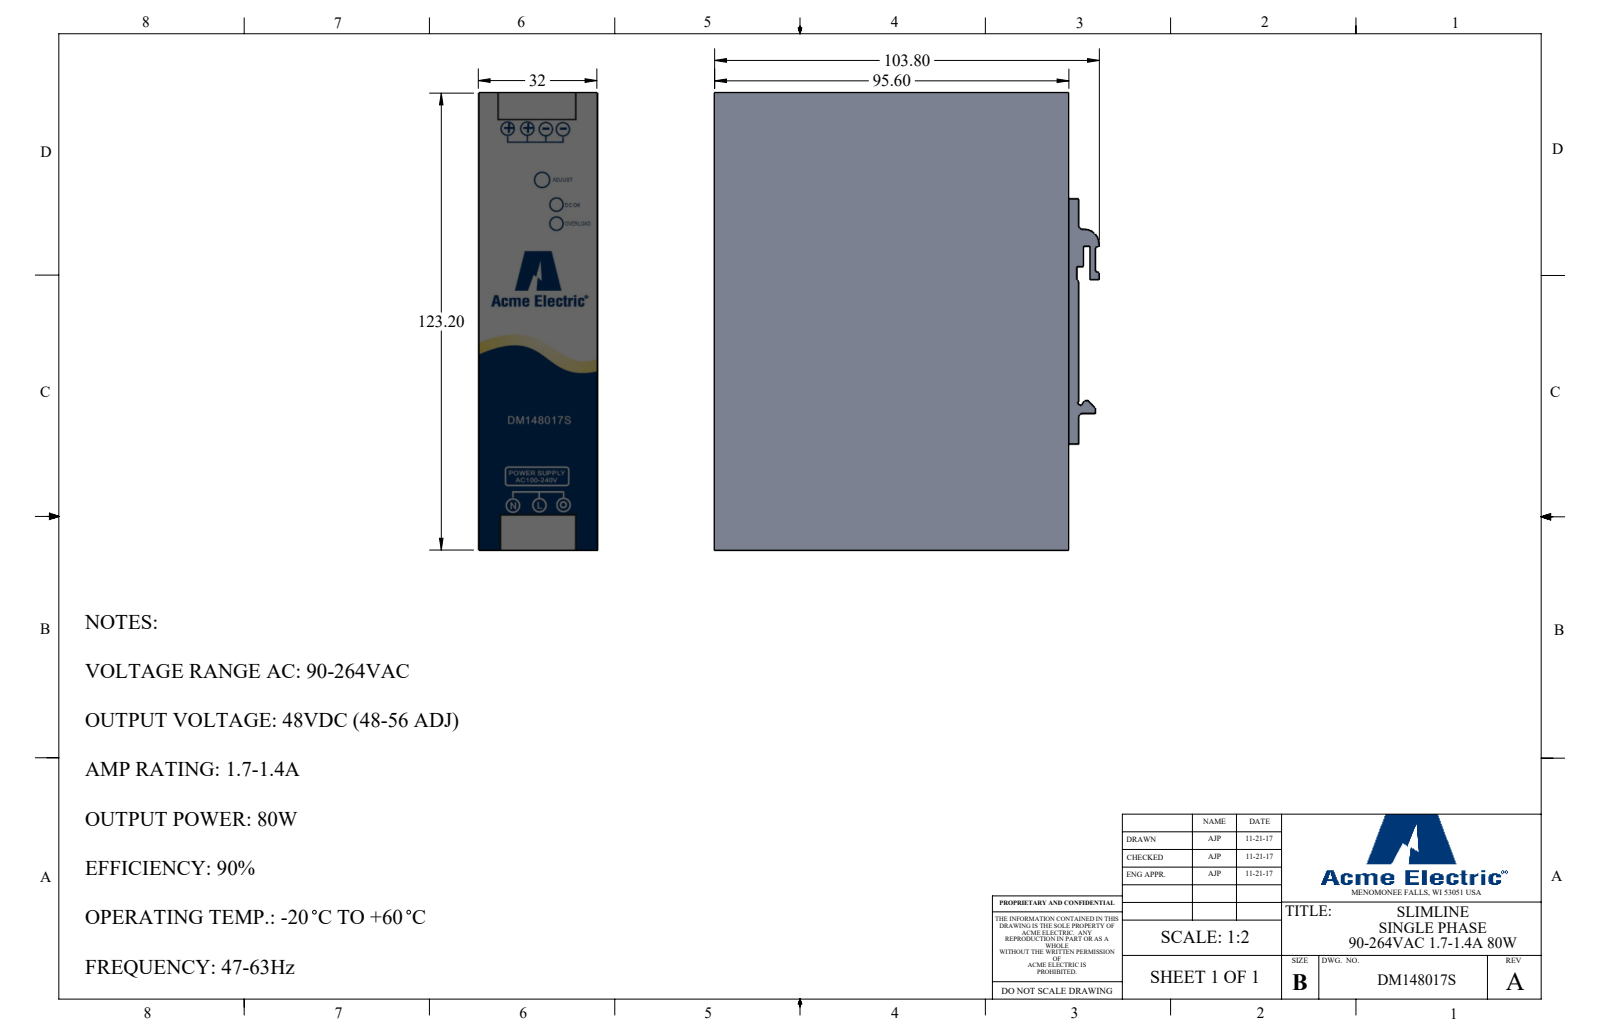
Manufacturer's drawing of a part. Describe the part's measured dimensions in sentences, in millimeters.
The part is named "DM148017S". Its 3-D file was written by "SolidWorks 2017 (AUTOMOTIVE_DESIGN)". It is 1 solid with 36 faces: 33 planar, 3 cylindrical and 0 other. Overall it measures 123.2 by 103.8 by 32 millimeters. Its volume is 383 924 cubic millimeters and its surface area 39 344 square millimeters. Partial cylindrical surfaces (rounded edges, fillets, slot ends): 2 of radius 1, 1 of radius 4. The main face-to-face distances are 32, 123.2, 95.6, 2.7, 98.3, 1.07, 30.93, 3, 5.7, 101.3.
